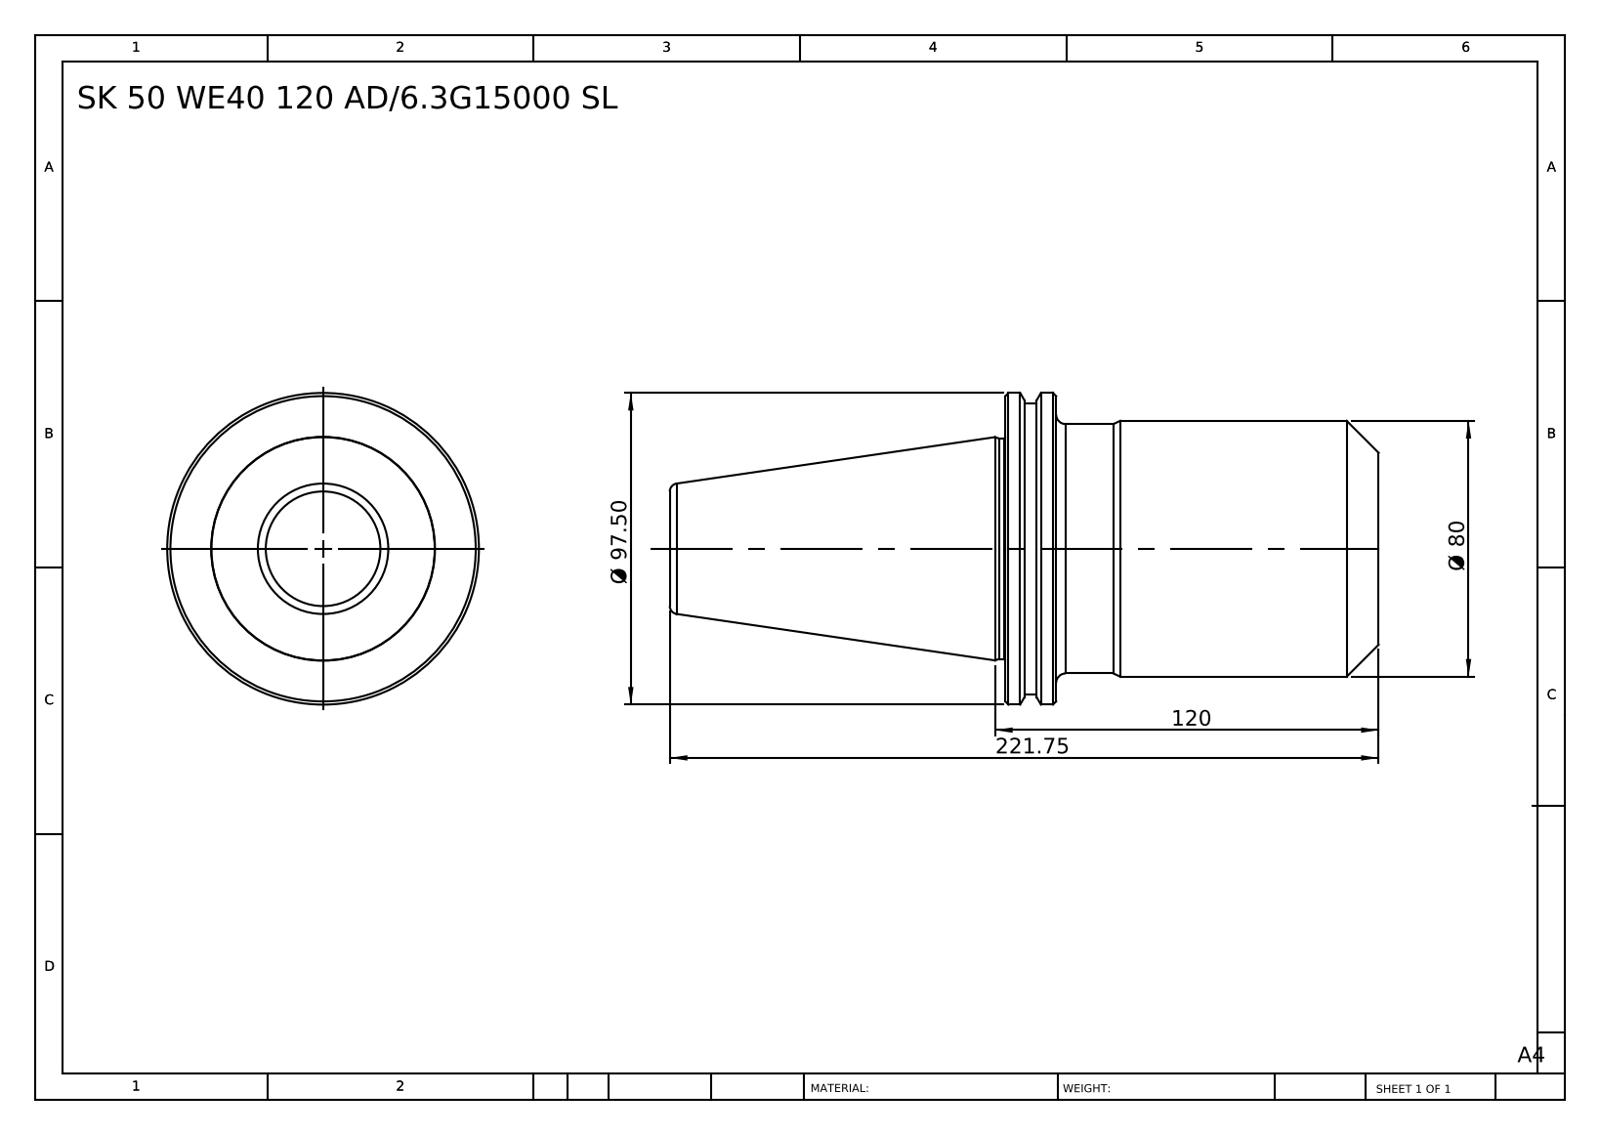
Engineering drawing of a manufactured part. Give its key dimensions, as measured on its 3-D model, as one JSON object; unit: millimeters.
{"part_name": "SK50 WE40 120 AD-6.3G15000 SL", "step_written_by": "SolidWorks 2014 (CONFIG_CONTROL_DESIGN)", "units": "millimeters", "bodies": {"solids": 1, "faces": 40, "planar": 6, "cylindrical": 12, "other": 22}, "overall_size": [221.75, 97.5, 97.5], "volume_mm3": 864868, "surface_area_mm2": 60163, "round_bosses_or_shafts": [[97.5, 1], [91, 1], [80, 1], [78, 1], [69, 1]], "face_to_face_distances": [116.8, 100.9, 15.9, 221.75, 120.85, 104.95, 107.02, 6.12, 9.78, 114.73]}
